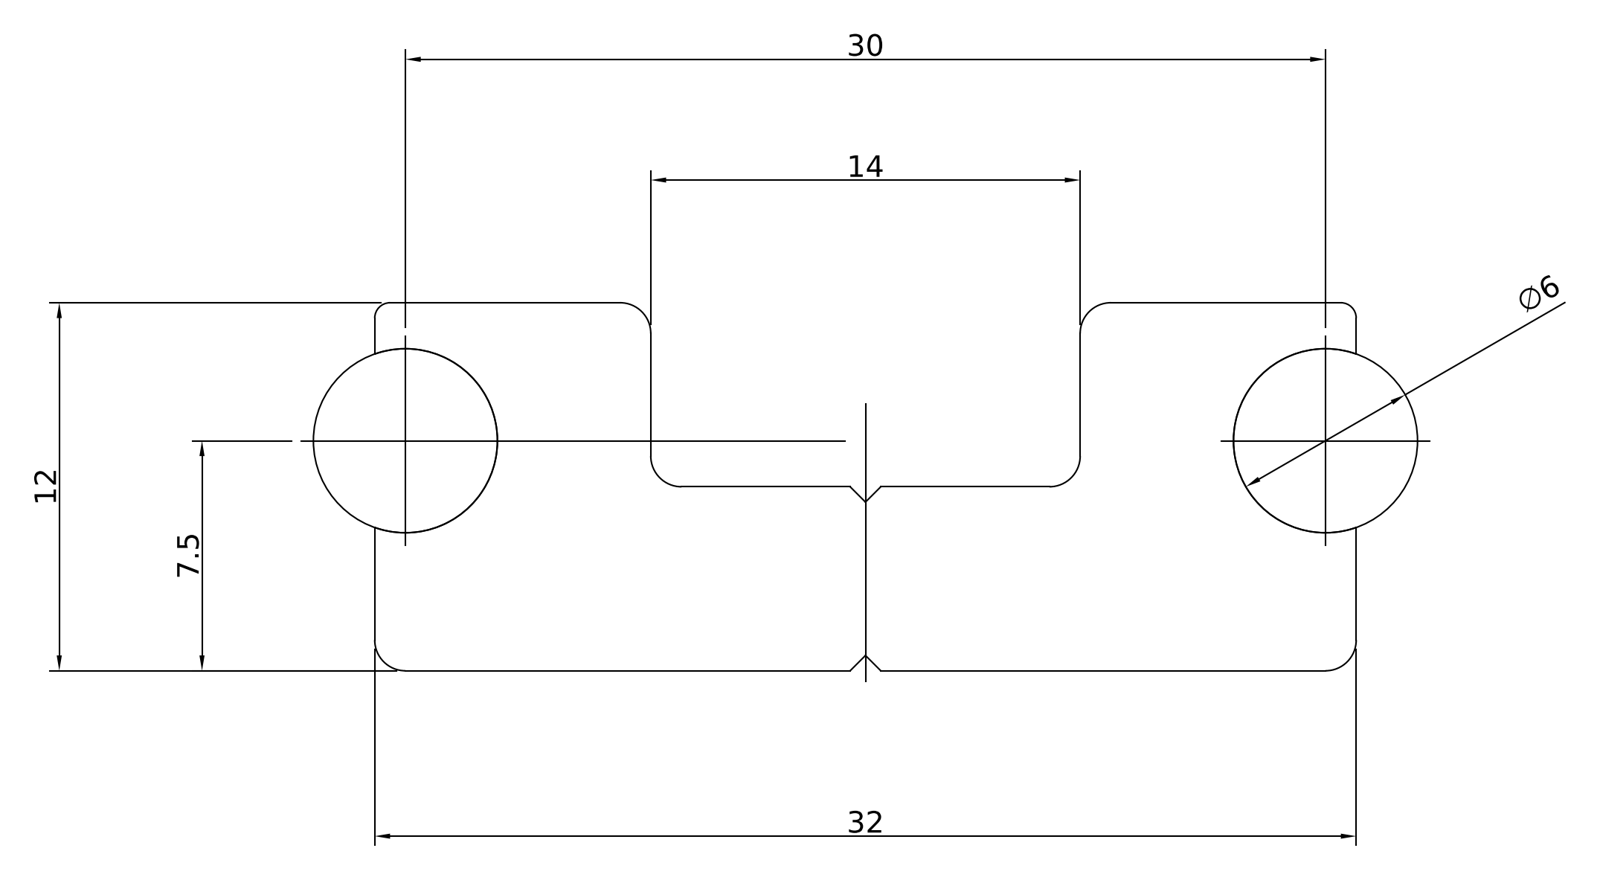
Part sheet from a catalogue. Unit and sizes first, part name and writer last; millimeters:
Units: millimetres
Overall size (bounding box): 1000 × 36 × 12
Round holes (diameter × count): ⌀6.5 ×10, ⌀6 ×2
Partial cylindrical surfaces — rounded edges, fillets, slot ends (radius × count): R1 ×6, R0.5 ×2
Main face-to-face distances: 6, 12, 9, 23, 32, 14, 3.54, 1000
Hole centre spacings: 100, 200, 300, 400, 500, 600, 700, 800
Volume: 312 318 mm³ · Surface area: 148 028 mm²
Bodies: 3 solids, 134 faces (102 planar, 22 cylindrical, 10 other)
Part name (STEP PRODUCT): 80PGL0001-A; 958510003988; 958510003989
STEP written by: Autodesk Inventor 2022 (AUTOMOTIVE_DESIGN)
